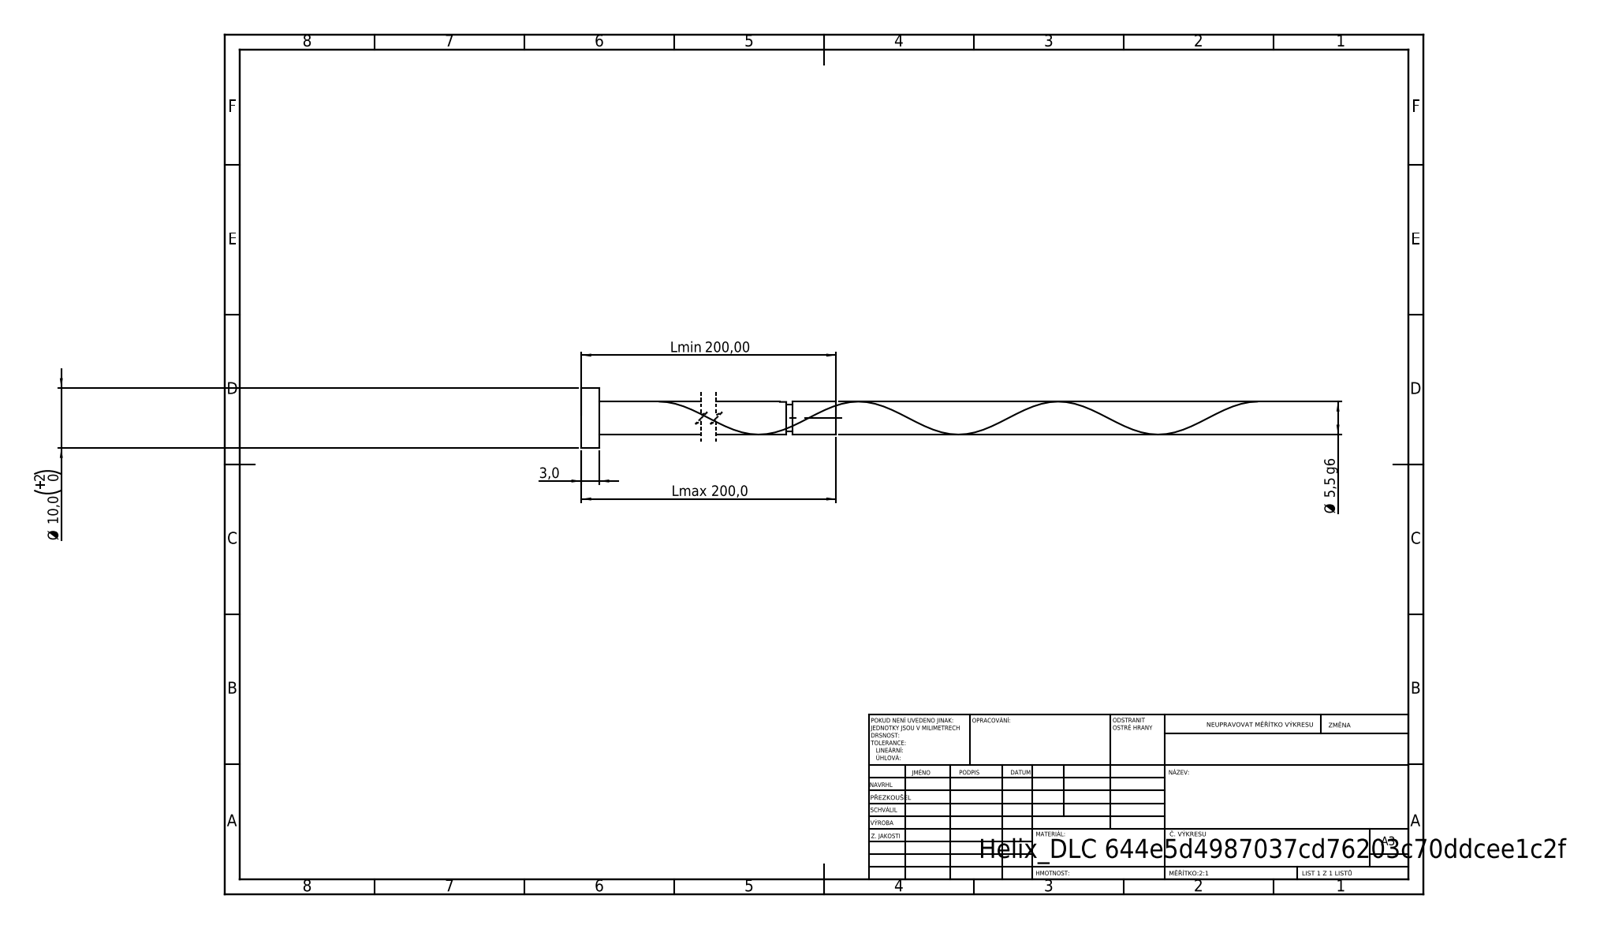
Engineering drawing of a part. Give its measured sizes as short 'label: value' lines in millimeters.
written by: SolidWorks 2019 (CONFIG_CONTROL_DESIGN)
unit: mm
bodies: 1 solid, 21 faces (6 planar, 14 cylindrical, 1 other)
size: 200 × 10 × 10
volume: 4 861 mm³; area: 3 730 mm²
bosses: 1× ⌀10, 1× ⌀5.5, 1× ⌀4.4
face distances: 3, 200, 197, 192.75, 189.75, 7.25, 191.65, 188.65, 1.1, 8.35
